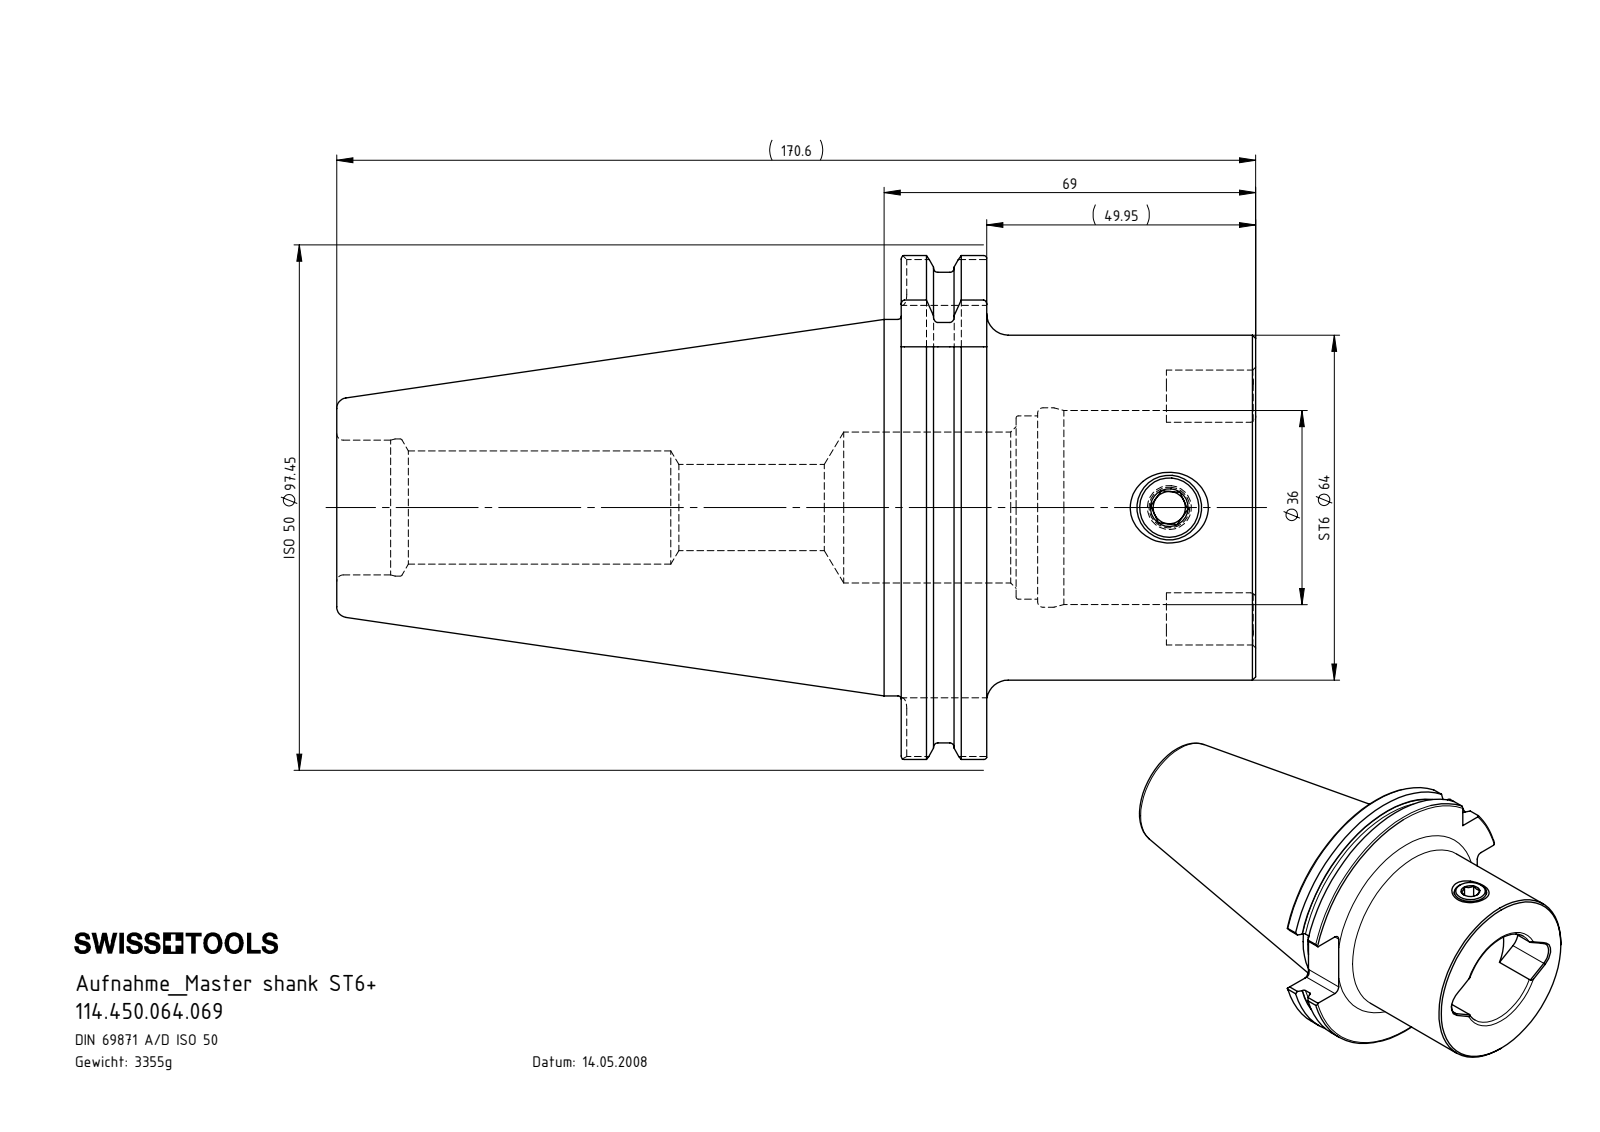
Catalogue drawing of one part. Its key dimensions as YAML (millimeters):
part_name: "SK5.ST6.K01.069; SK5-ST6.K01.069_B; ST6-ER1.001.018_A"
step_written_by: "SolidWorks 2017 (AUTOMOTIVE_DESIGN)"
units: millimeters
bodies: {solids: 2, faces: 132, planar: 55, cylindrical: 32, other: 45}
overall_size: [170.6, 97.45, 93.51]
volume: 427408
surface_area: 59609
round_holes:
  - {diameter: 6, count: 1}
  - {diameter: 11, count: 1}
  - {diameter: 16, count: 1}
  - {diameter: 21, count: 1}
  - {diameter: 25, count: 1}
  - {diameter: 25.45, count: 1}
  - {diameter: 28, count: 1}
  - {diameter: 34, count: 1}
  - {diameter: 36, count: 1}
  - {diameter: 37, count: 1}
round_bosses_or_shafts:
  - {diameter: 91, count: 1}
  - {diameter: 69.85, count: 1}
  - {diameter: 64, count: 1}
  - {diameter: 12, count: 1}
partial_cylinders:
  - {radius: 2, count: 8}
  - {radius: 5.2, count: 2}
  - {radius: 48.73, count: 1}
face_to_face_distances: [15.85, 65.8, 49.95, 104.8, 120.65, 170.6, 72.8, 30.7, 25.7, 154]
